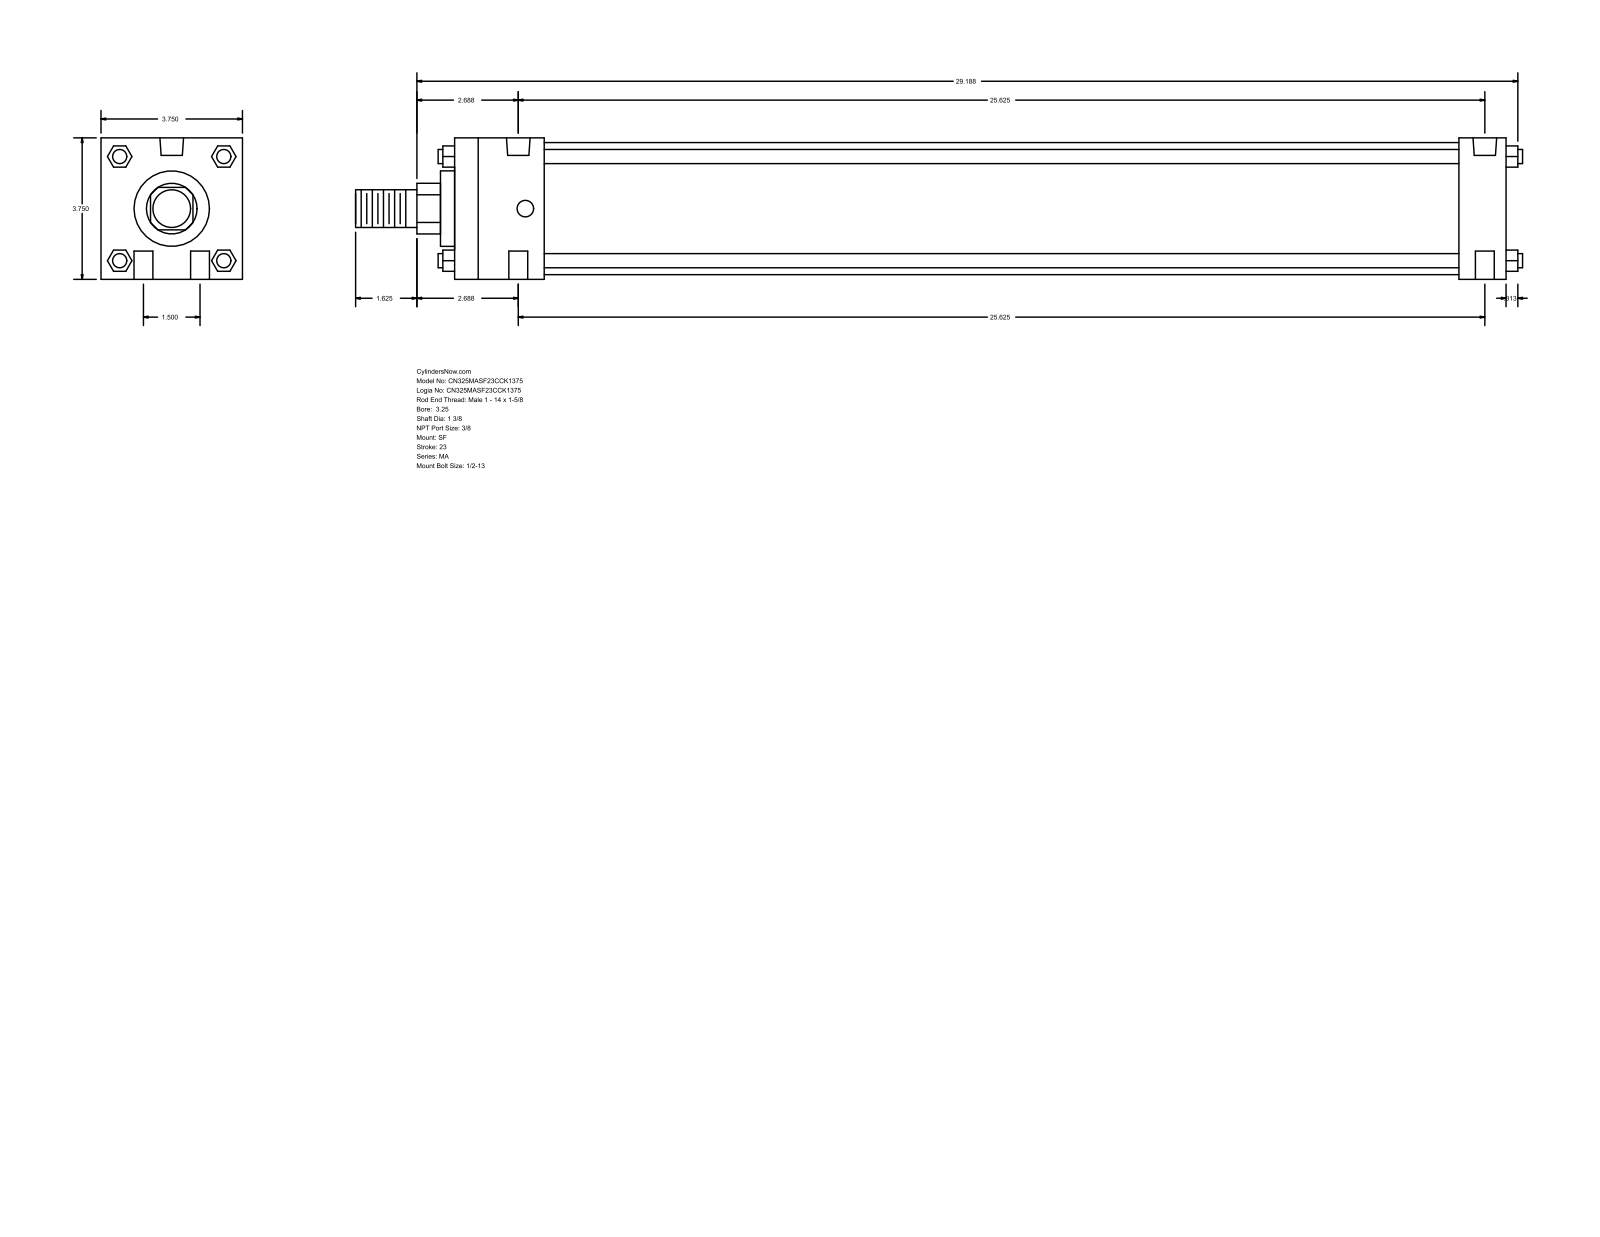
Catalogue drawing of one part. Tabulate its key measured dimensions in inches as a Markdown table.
| quantity | value |
| --- | --- |
| part name | MA_SF__0325_1.375 |
| STEP written by | GSSL Pune (CONFIG_CONTROL_DESIGN) |
| units | inches |
| bodies | 0 solids, 124 faces (94 planar, 30 cylindrical, 0 other) |
| overall size | 30.937 × 3.75 × 3.75 |
| round holes (diameter × count) | 0.5 × 4, 0.437 × 2, 0.627 × 2 |
| round bosses / shafts (diameter × count) | 0.375 × 4, 3.5 × 1, 2 × 1, 1.375 × 1, 1 × 1 |
| partial cylindrical surfaces (radius × count) | 0.672 × 1 |
| main face-to-face distances | 3.75, 27.875, 26.625, 1.25, 2.375, 24.25, 25.5, 0.375, 2.75, 27 |
| hole center spacings | 0.75, 25.636, 25.625, 1.5, 25.669, 25.25 |
